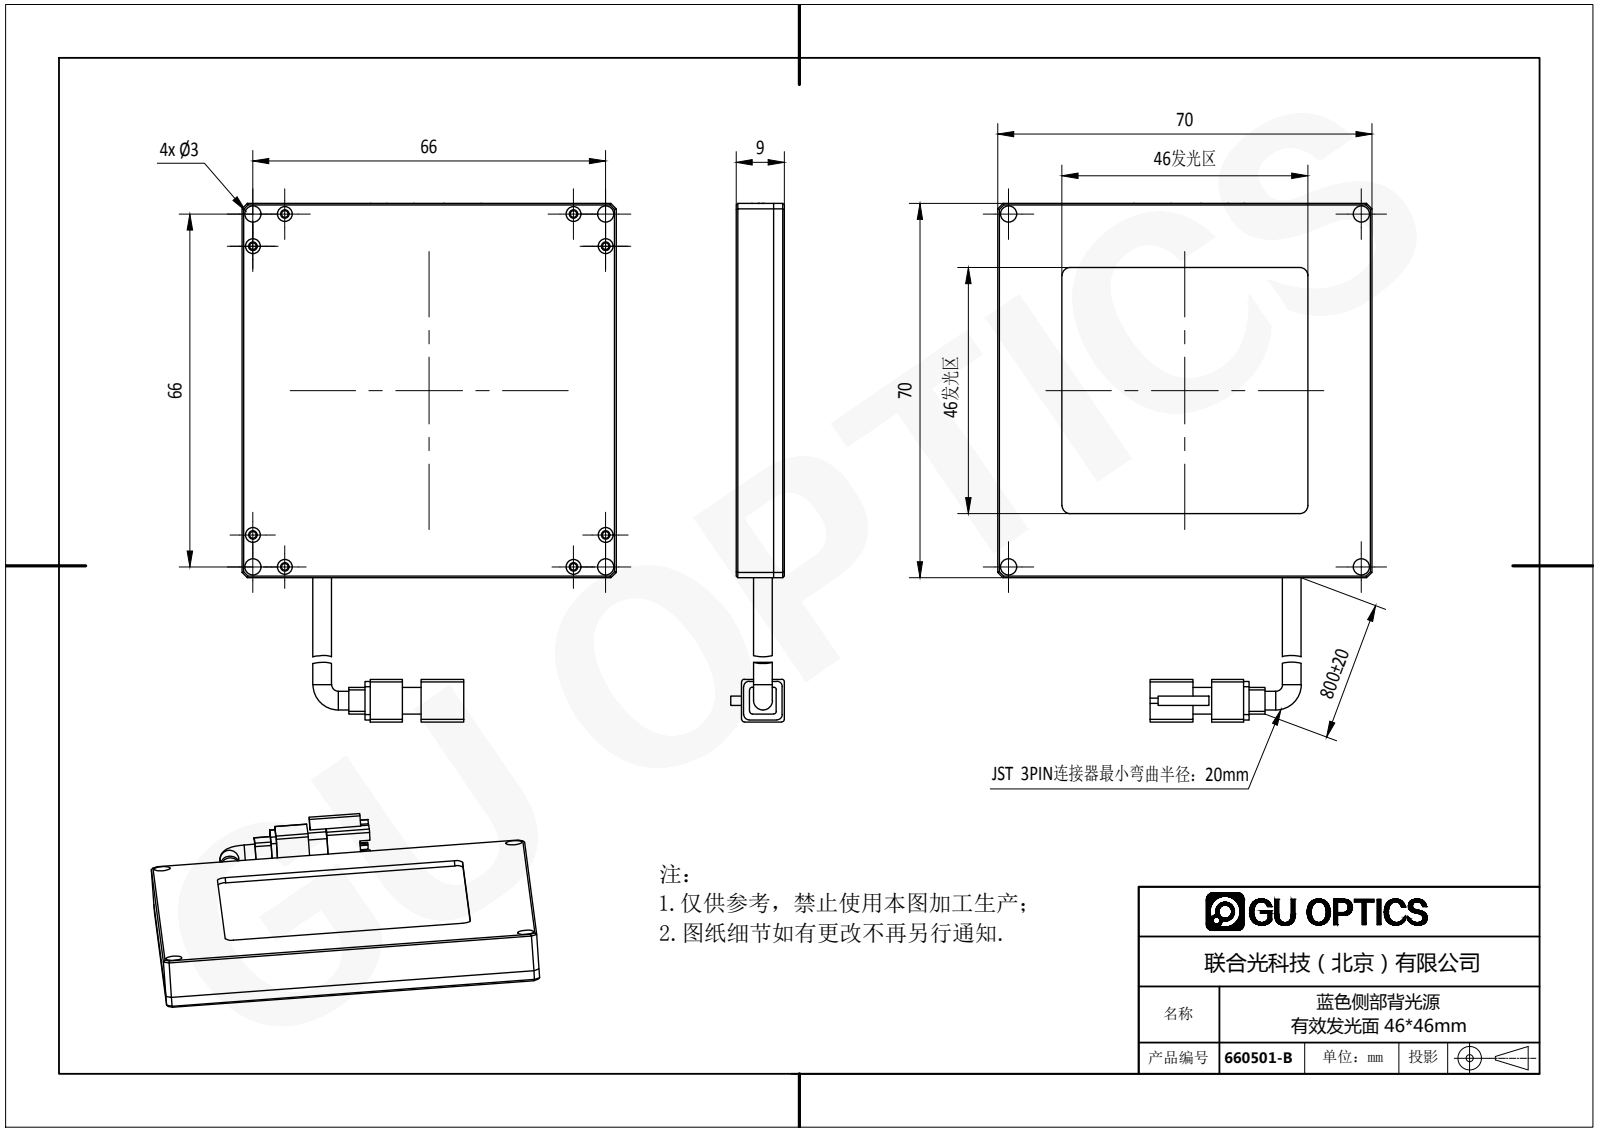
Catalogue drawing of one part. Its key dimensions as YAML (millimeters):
part_name: "660501-B"
step_written_by: "SolidWorks 2016 (AUTOMOTIVE_DESIGN)"
units: millimeters
bodies: {solids: 6, faces: 436, planar: 245, cylindrical: 114, other: 77}
overall_size: [97, 70, 10]
volume: 39909
surface_area: 30038
round_holes:
  - {diameter: 1.6, count: 10}
  - {diameter: 1.25, count: 8}
  - {diameter: 2.8, count: 8}
  - {diameter: 3, count: 4}
round_bosses_or_shafts:
  - {diameter: 3.5, count: 2}
partial_cylinders:
  - {radius: 0.5, count: 8}
  - {radius: 2, count: 6}
  - {radius: 1, count: 4}
  - {radius: 1.5, count: 4}
face_to_face_distances: [6, 2, 8, 1, 7, 9, 4, 66, 64, 60]
hole_center_spacings: [66, 60.3, 66.27, 89.2, 6, 60, 85.28, 8.49]
